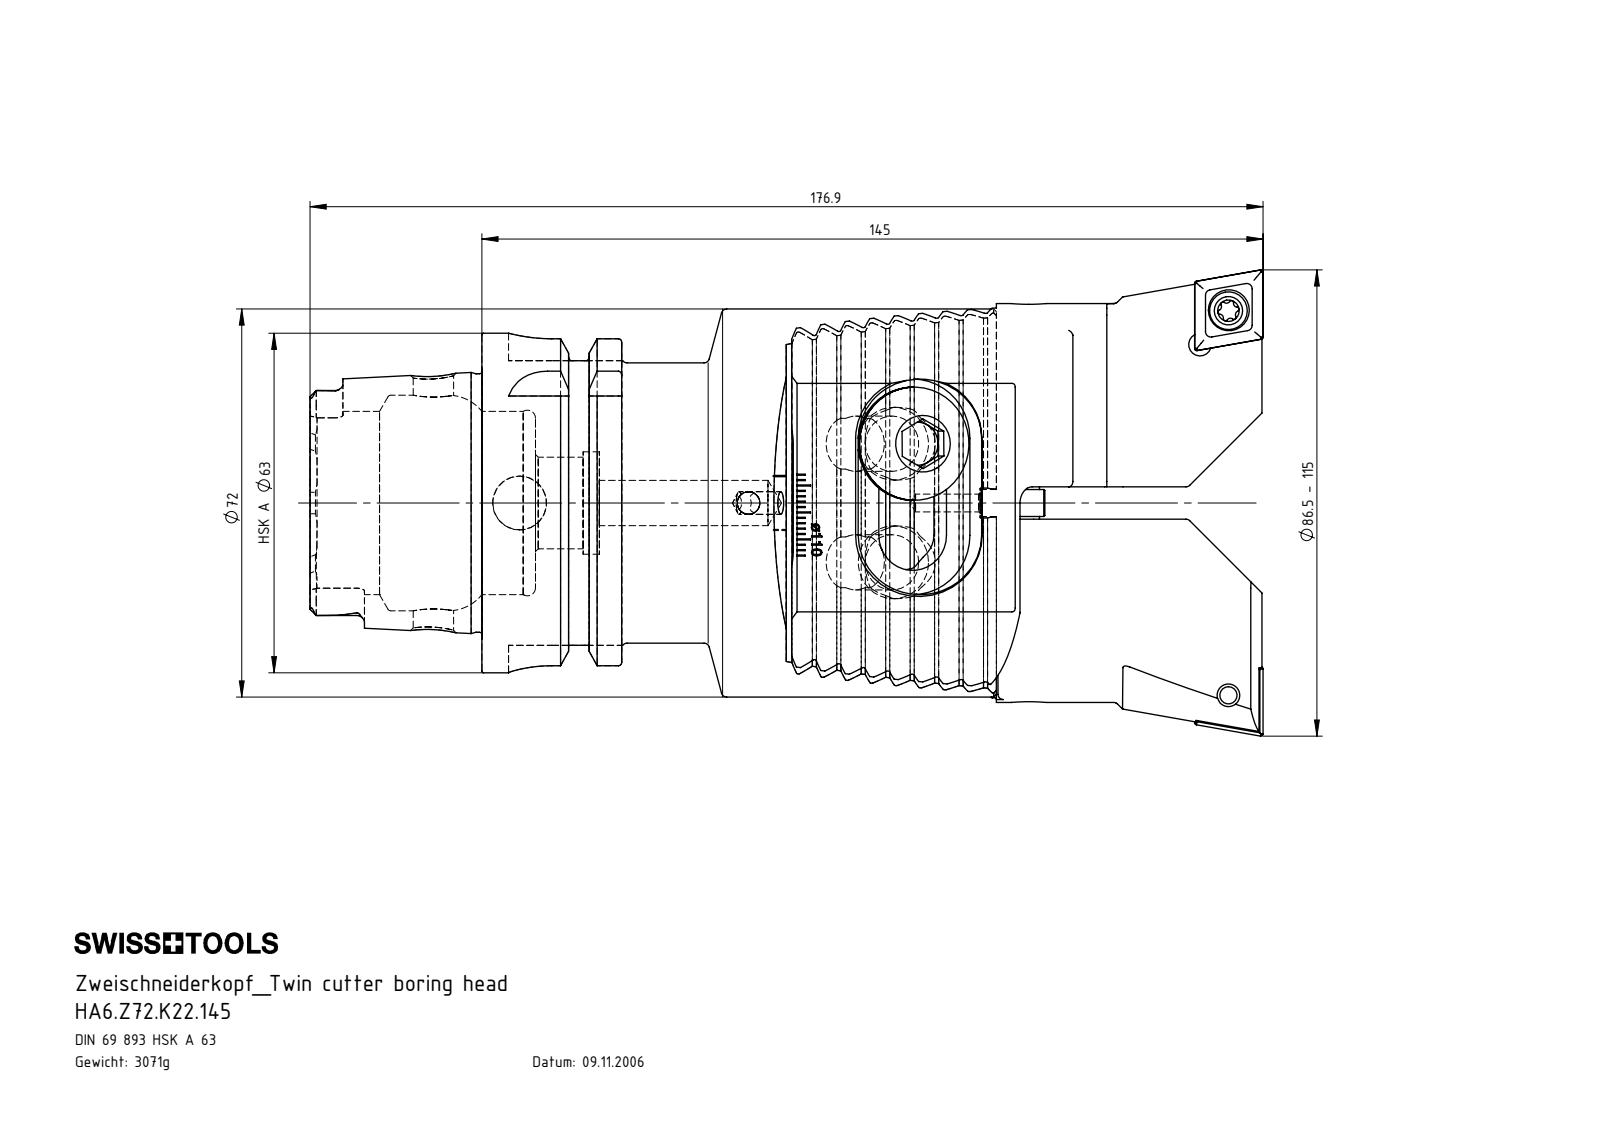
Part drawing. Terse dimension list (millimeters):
name: CCMT120404; HA6.Z72.K22.145; Z72-xxx.001.050_C; Z72-ER3.001.030 (+6 more)
written by: SolidWorks 2022 (CONFIG_CONTROL_DESIGN)
unit: mm
bodies: 13 solids, 1137 faces (570 planar, 259 cylindrical, 308 other)
size: 176.9 × 86.5 × 72
volume: 391 803 mm³; area: 87 035 mm²
holes: 4× ⌀4.2, 4× ⌀5, 2× ⌀2, 2× ⌀5.5, 2× ⌀7.6, 2× ⌀10.25, 2× ⌀13, 2× ⌀13.5, 1× ⌀3.3, 1× ⌀7.5, 1× ⌀8.4, 1× ⌀10
bosses: 2× ⌀21, 2× ⌀12, 2× ⌀7, 2× ⌀5, 1× ⌀72, 1× ⌀63, 1× ⌀54.95, 1× ⌀52
rounds: 18× R0.34, 16× R0.34, 16× R1, 12× R0.39, 12× R0.69, 6× R1.4, 6× R3, 4× R2.88
face distances: 4.07, 8.14, 12.21, 16.28, 4.01, 24.43, 20.36, 4.13, 20.35, 29.4
hole spacings: 8.21, 8.33, 20, 65.26, 65.36, 71.43, 88.8, 95.96
